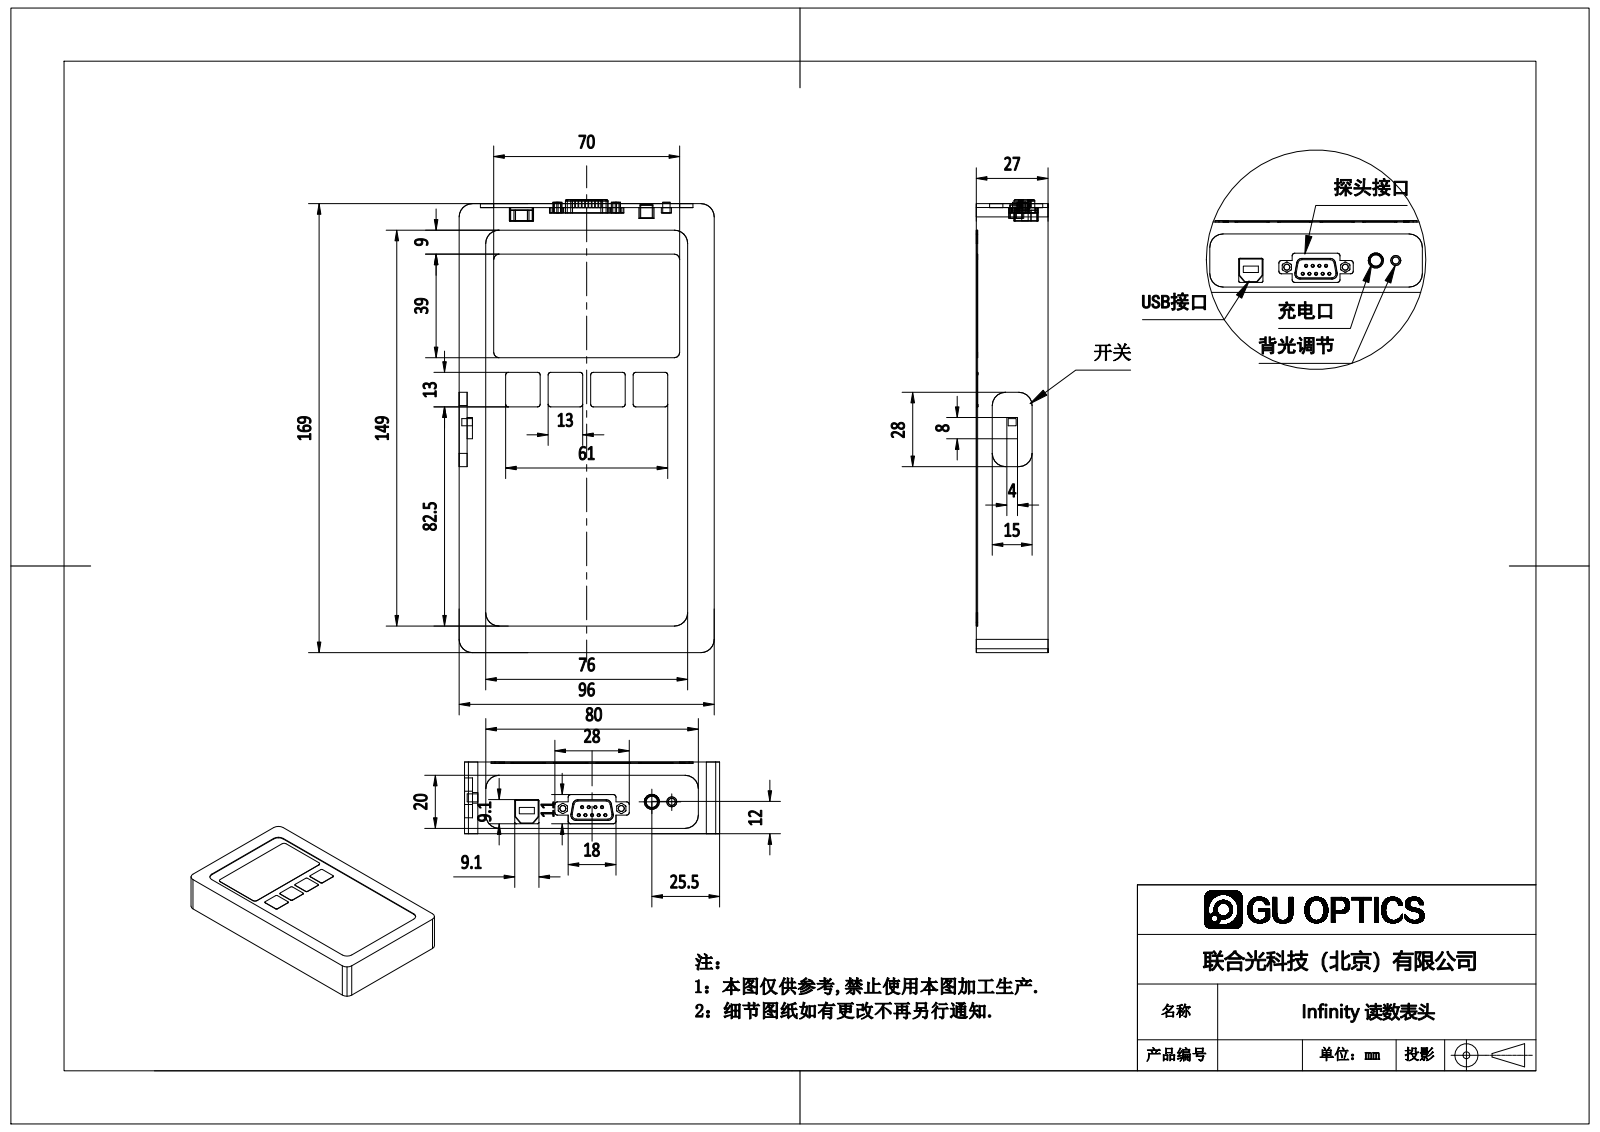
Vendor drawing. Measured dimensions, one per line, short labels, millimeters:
written by: SolidWorks 2020 (CONFIG_CONTROL_DESIGN)
unit: mm
bodies: 1 solid, 293 faces (129 planar, 140 cylindrical, 24 other)
size: 170.5 × 96 × 27
volume: 428 332 mm³; area: 48 741 mm²
holes: 9× ⌀1, 2× ⌀2.3, 1× ⌀3.8, 1× ⌀4.35, 1× ⌀5.7
bosses: 1× ⌀4.92, 1× ⌀2.76
rounds: 24× R1, 20× R0.5, 16× R5, 8× R2
face distances: 26.5, 0.5, 27, 96, 26.6, 0.4, 167.5, 1.5, 169, 26.7
hole spacings: 3.25, 2.5, 4.8, 5, 6.93, 7.5, 6.5, 7.27
